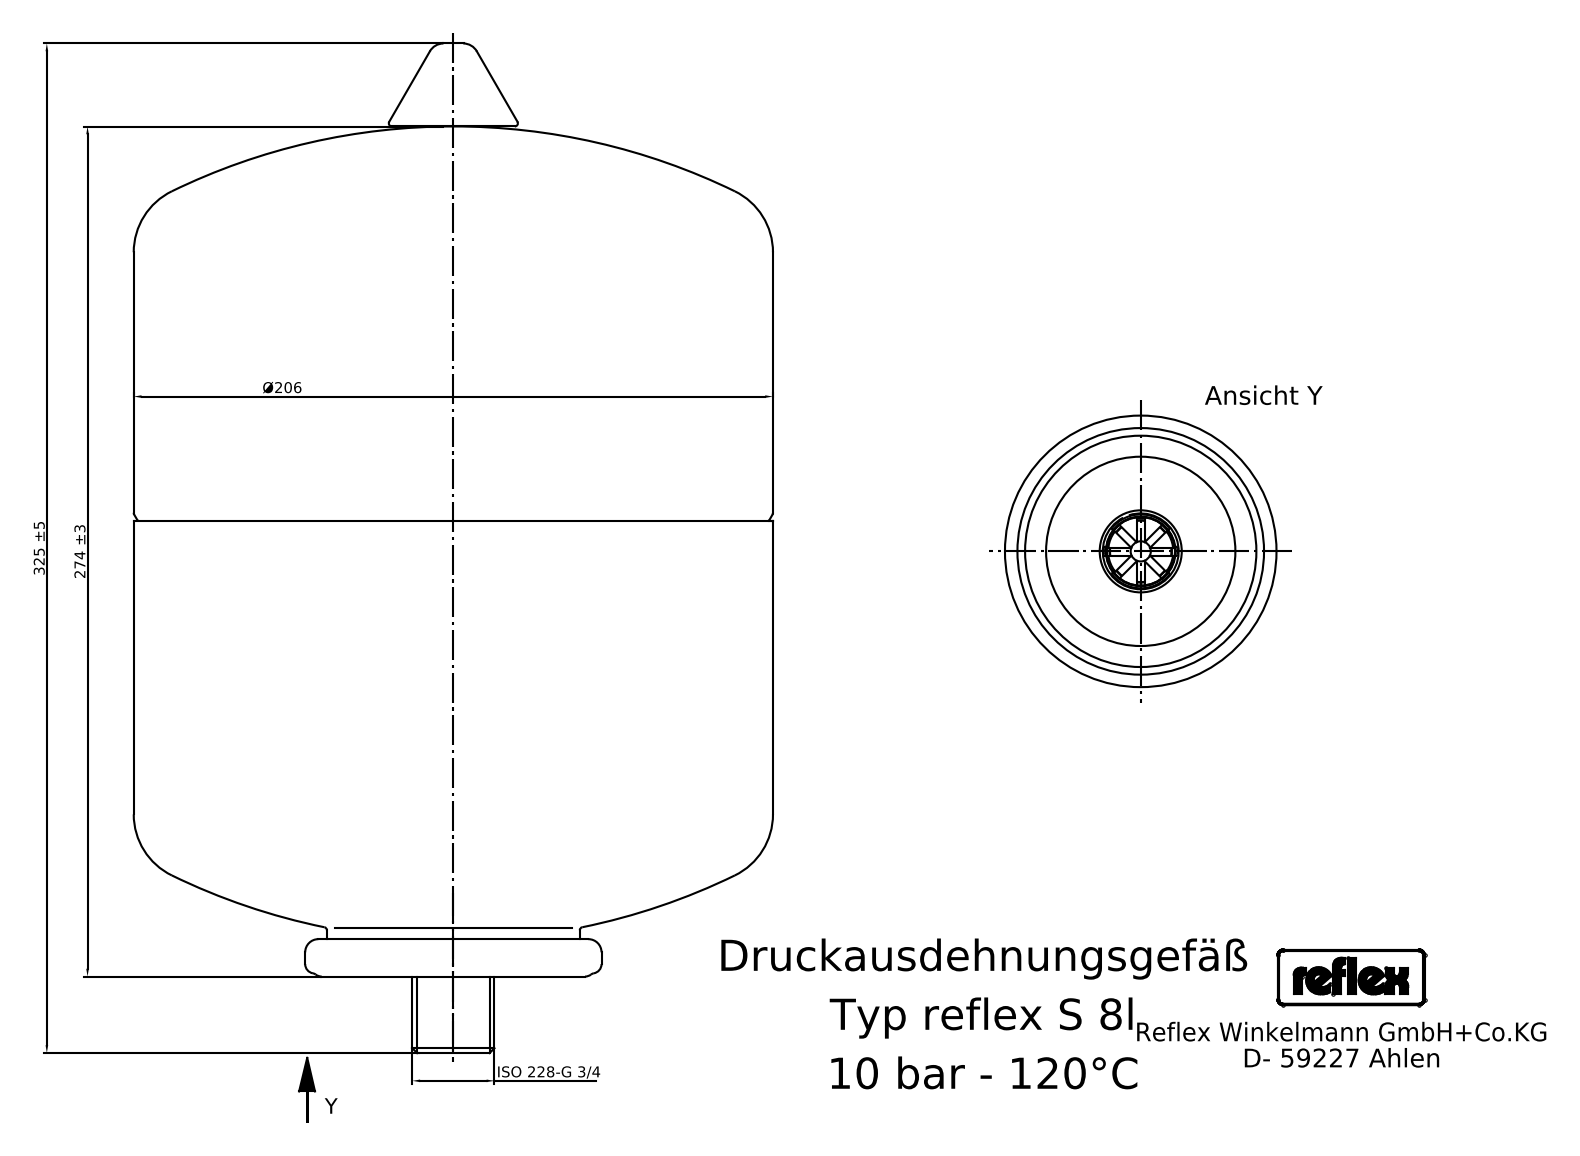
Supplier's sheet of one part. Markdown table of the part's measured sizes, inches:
| quantity | value |
| --- | --- |
| STEP written by | Mechanical Desktop 2008 (CONFIG_CONTROL_DESIGN) |
| units | inches |
| bodies | 13 solids, 151 faces (71 planar, 46 cylindrical, 34 other) |
| overall size | 12.795 × 8.123 × 8.11 |
| volume | 480.9 in³ |
| surface area | 572 in² |
| round holes (diameter × count) | 0.555 × 1, 0.744 × 1 |
| round bosses / shafts (diameter × count) | 8.11 × 1, 3.78 × 1, 3.228 × 1, 1.059 × 1, 0.673 × 1, 0.354 × 1, 0.236 × 1 |
| partial cylindrical surfaces (radius × count) | 0.044 × 4, 0.018 × 3, 0.03 × 2, 0.053 × 2, 0.073 × 2, 0.074 × 2, 0.1 × 2, 0.022 × 1 |
| main face-to-face distances | 7.126, 1.299, 8.425, 0.512, 1.811, 8.937, 5.295, 4.783, 3.484, 3.642 |
